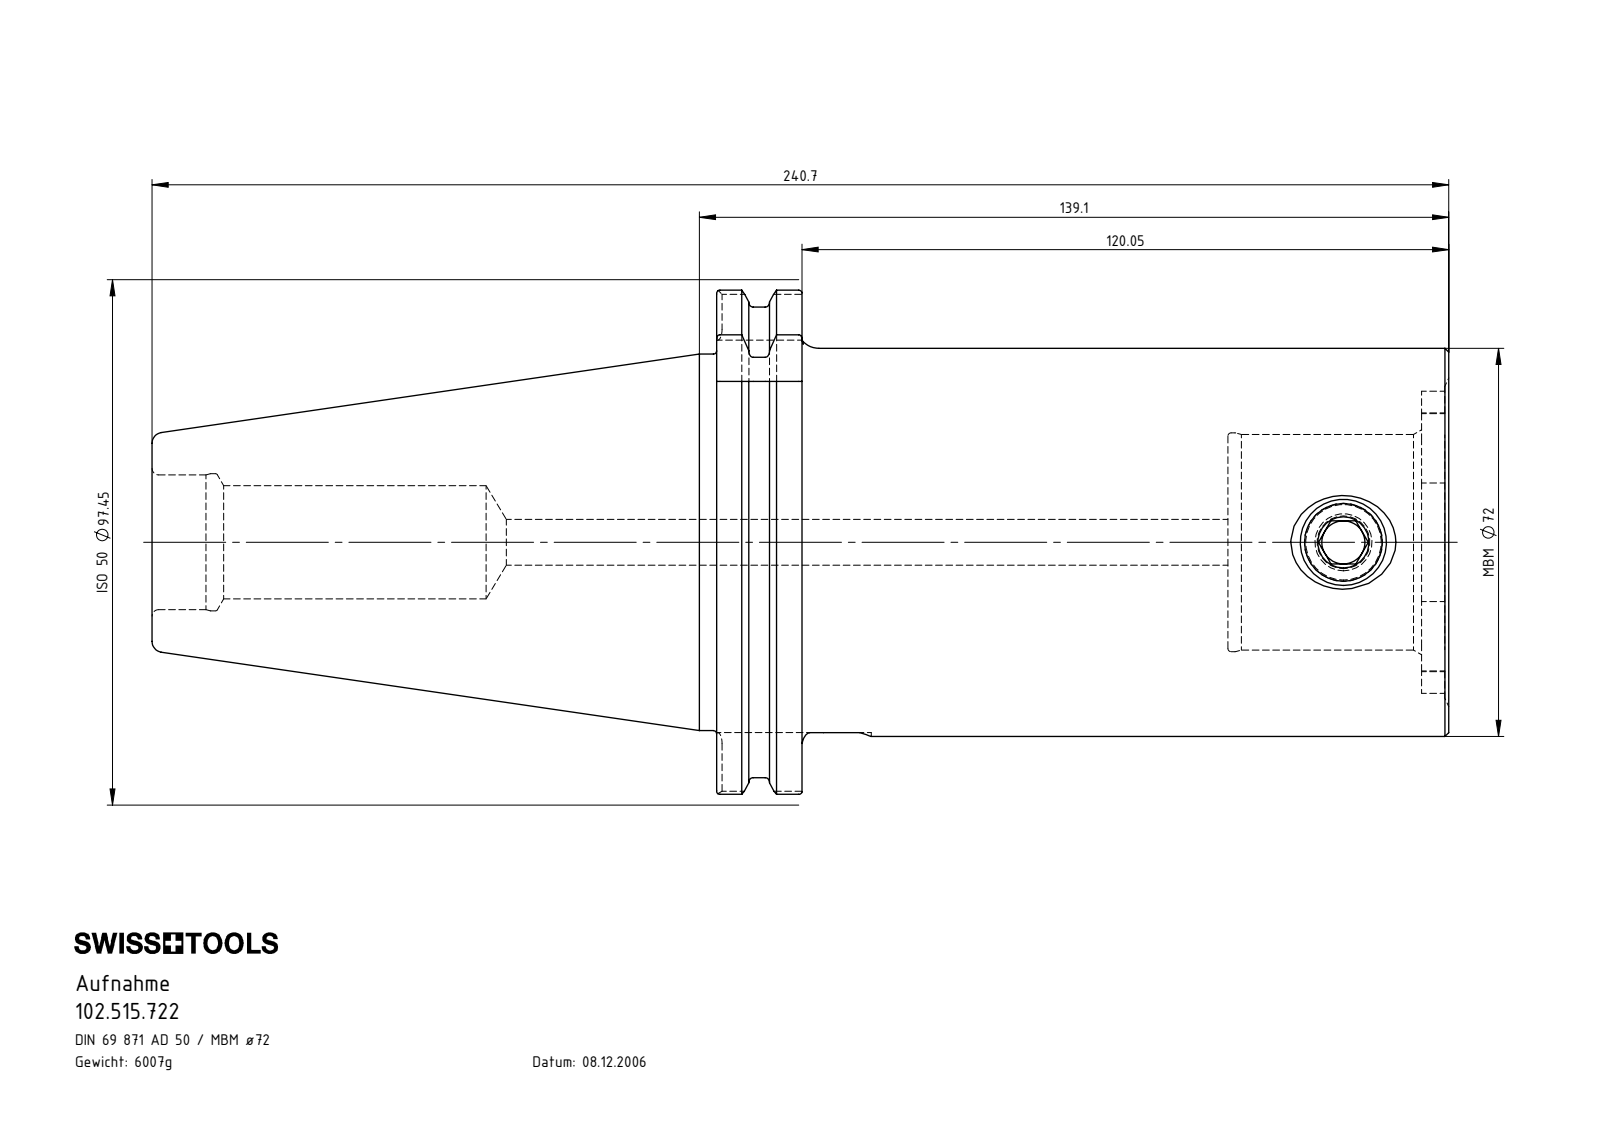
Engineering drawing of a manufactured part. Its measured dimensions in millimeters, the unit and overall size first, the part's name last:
Units: millimetres
Overall size (bounding box): 240.7 × 97.45 × 93.51
Round holes (diameter × count): ⌀8 ×1, ⌀8.5 ×1, ⌀14.5 ×1, ⌀21 ×1, ⌀25 ×1, ⌀25.45 ×1, ⌀40 ×1, ⌀40.6 ×1
Round bosses / shafts (diameter × count): ⌀91 ×1, ⌀72 ×1, ⌀69.85 ×1, ⌀16 ×1
Partial cylindrical surfaces — rounded edges, fillets, slot ends (radius × count): R2 ×8, R5.2 ×4, R12.85 ×1, R23.75 ×1, R28.02 ×1, R48.73 ×1
Main face-to-face distances: 15.85, 94.9, 79.05, 135.9, 120.05, 41, 130.85, 115, 35.95, 5.05
Volume: 765 191 mm³ · Surface area: 77 055 mm²
Bodies: 2 solids, 174 faces (56 planar, 51 cylindrical, 67 other)
Part name (STEP PRODUCT): SK5-MB7.K01.139_C; MB7-ER1.001.022_A; 102.515.722
STEP written by: SolidWorks 2017 (CONFIG_CONTROL_DESIGN)
